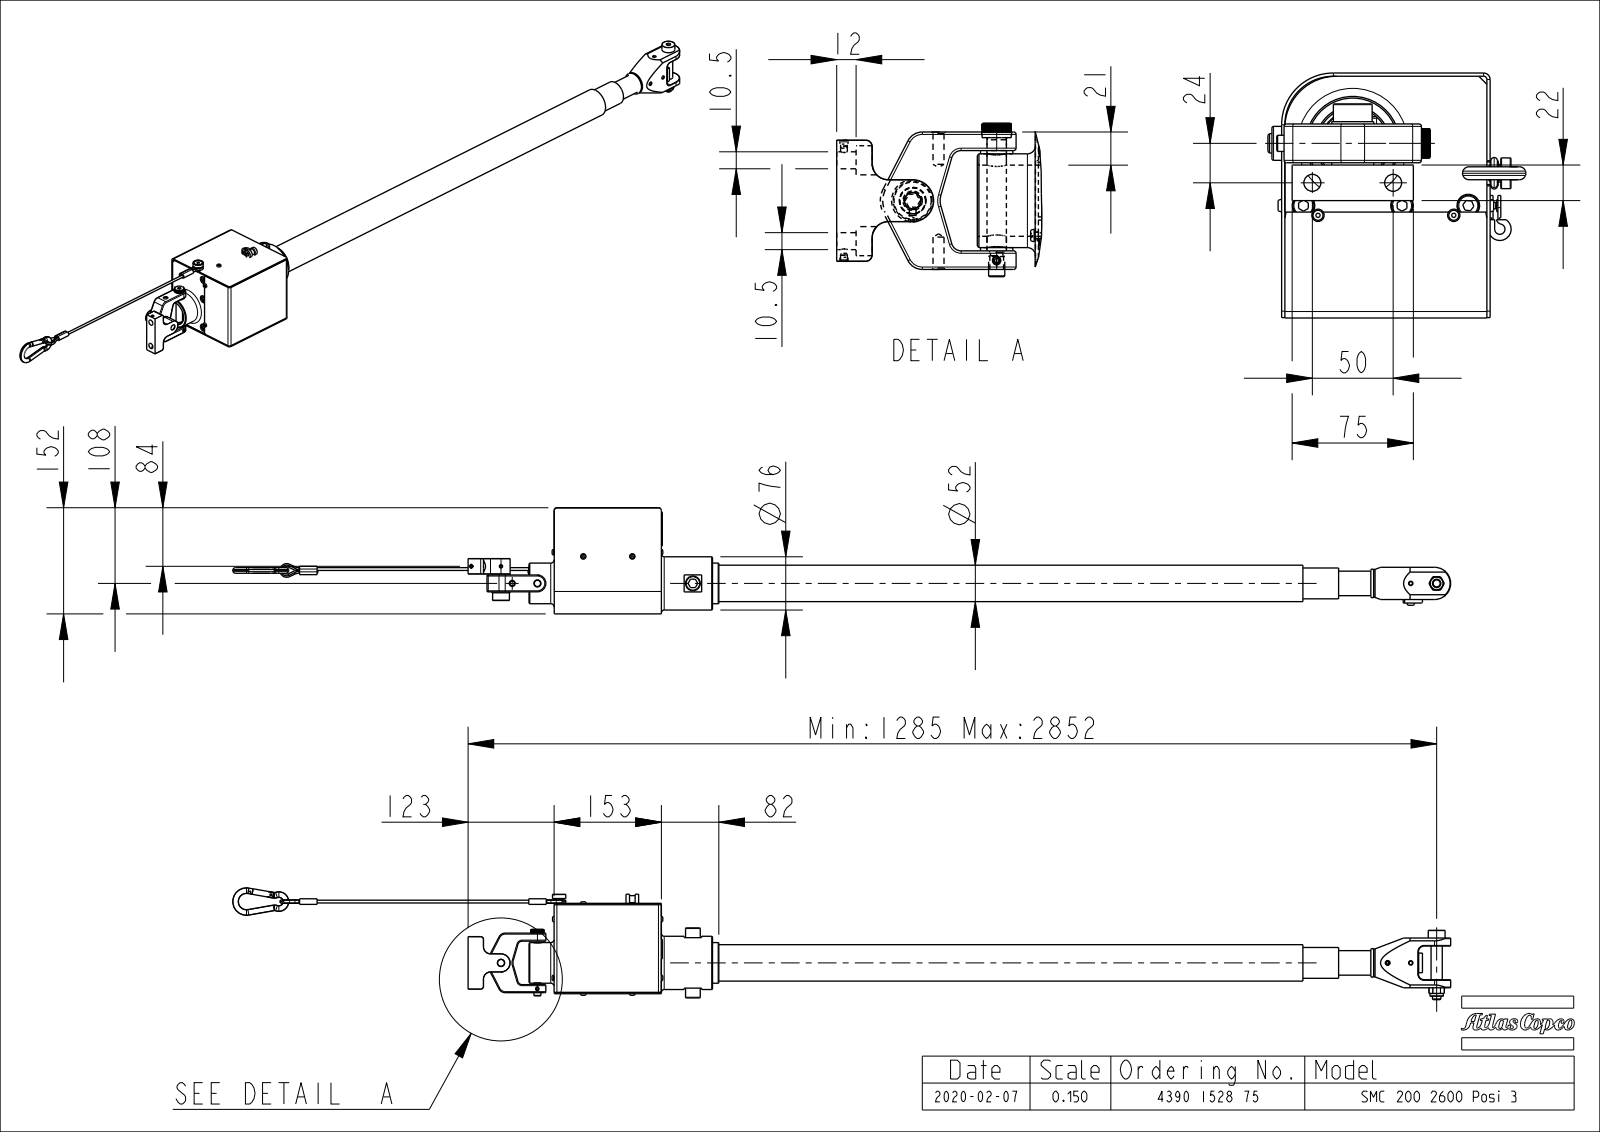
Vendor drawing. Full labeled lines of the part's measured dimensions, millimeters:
Part name (STEP PRODUCT): 4390208513; 4390208523; 0211132500; 4390208500_ASM (+8 more)
STEP written by: CREO PARAMETRIC BY PTC INC, 2018100 (AP242_MANAGED_MODEL_BASED_3D_ENGINEERING_MIM_LF)
Units: millimetres
Bodies: 64 solids, 4173 faces (1358 planar, 1235 cylindrical, 1580 other)
Overall size (bounding box): 1739.02 × 159.62 × 151.5
Volume: 1 926 000 mm³ · Surface area: 1 279 000 mm²
Round holes (diameter × count): ⌀4 ×7, ⌀5 ×7, ⌀3.3 ×6, ⌀6 ×5, ⌀8.5 ×4, ⌀12 ×4, ⌀4.2 ×3, ⌀14 ×3, ⌀2.87 ×2, ⌀3 ×2, ⌀6.8 ×2, ⌀10 ×2
Round bosses / shafts (diameter × count): ⌀4 ×13, ⌀8 ×12, ⌀4.8 ×6, ⌀2.55 ×6, ⌀13 ×3, ⌀10 ×3, ⌀3.5 ×3, ⌀24 ×2
Partial cylindrical surfaces — rounded edges, fillets, slot ends (radius × count): R0.2 ×147, R0.5 ×89, R2 ×28, R1.5 ×24, R0.3 ×15, R1 ×12, R4 ×10, R0.2 ×4
Main face-to-face distances: 2, 127, 149.5, 129, 125, 30, 147.5, 151, 28, 151.5
Hole centre spacings: 9.22, 9.97, 10.82, 15.13, 16, 34.59, 34.93, 48.73
